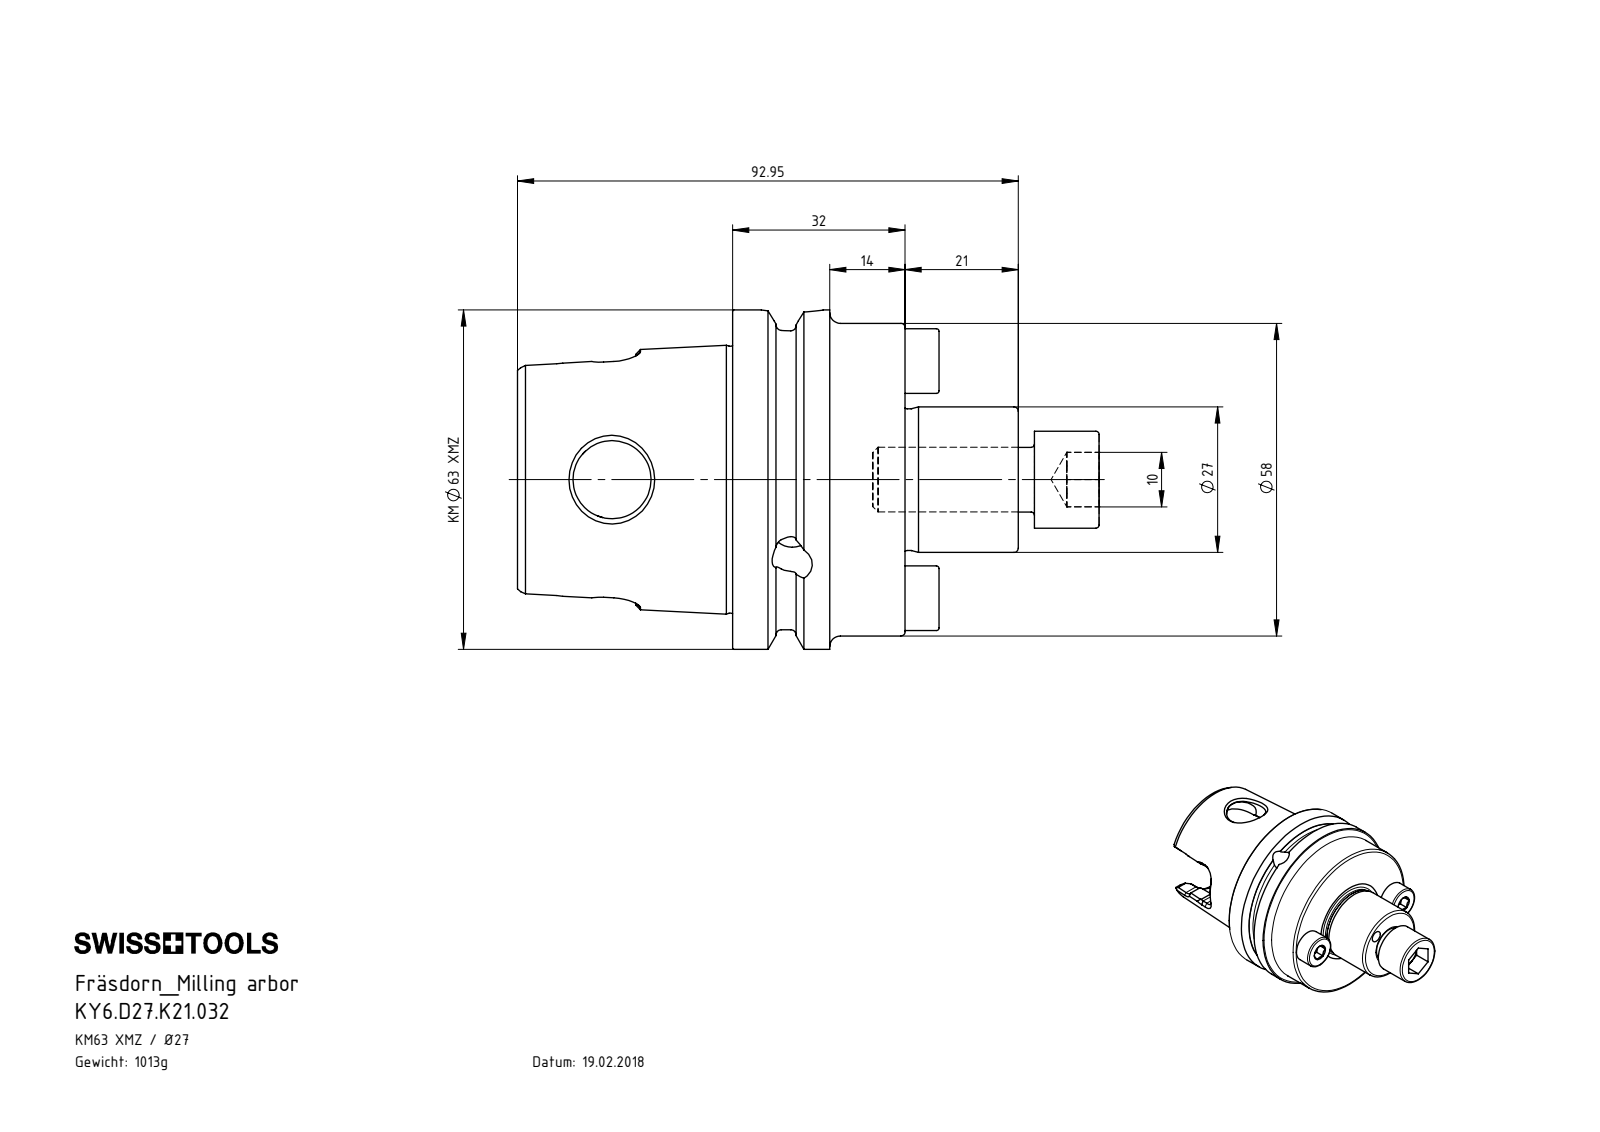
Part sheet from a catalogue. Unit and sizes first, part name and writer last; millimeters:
Units: millimetres
Overall size (bounding box): 107.95 × 62.95 × 62.95
Round holes (diameter × count): ⌀4.2 ×3, ⌀10 ×3, ⌀5 ×2, ⌀7.47 ×2, ⌀8 ×1, ⌀8.48 ×1, ⌀10.25 ×1, ⌀11.5 ×1, ⌀13 ×1, ⌀14.5 ×1, ⌀31.1 ×1, ⌀35.27 ×1
Round bosses / shafts (diameter × count): ⌀12 ×3, ⌀6 ×2, ⌀4.6 ×2, ⌀62.95 ×1, ⌀58 ×1, ⌀55.7 ×1, ⌀27 ×1, ⌀26.3 ×1
Partial cylindrical surfaces — rounded edges, fillets, slot ends (radius × count): R4 ×6, R3.5 ×2, R7.04 ×2
Main face-to-face distances: 32, 1.1, 33.1, 6, 21, 54.1, 53, 38, 36, 74
Hole centre spacings: 10, 16.52, 22, 29.92, 20, 44
Volume: 129 010 mm³ · Surface area: 31 704 mm²
Bodies: 4 solids, 384 faces (87 planar, 102 cylindrical, 195 other)
Part name (STEP PRODUCT): D27-ER2.001.021_B; KY6-D27.K21.032_A; D27-ER1.002.030_A; KY6.D27.K21.032
STEP written by: SolidWorks 2017 (CONFIG_CONTROL_DESIGN)
